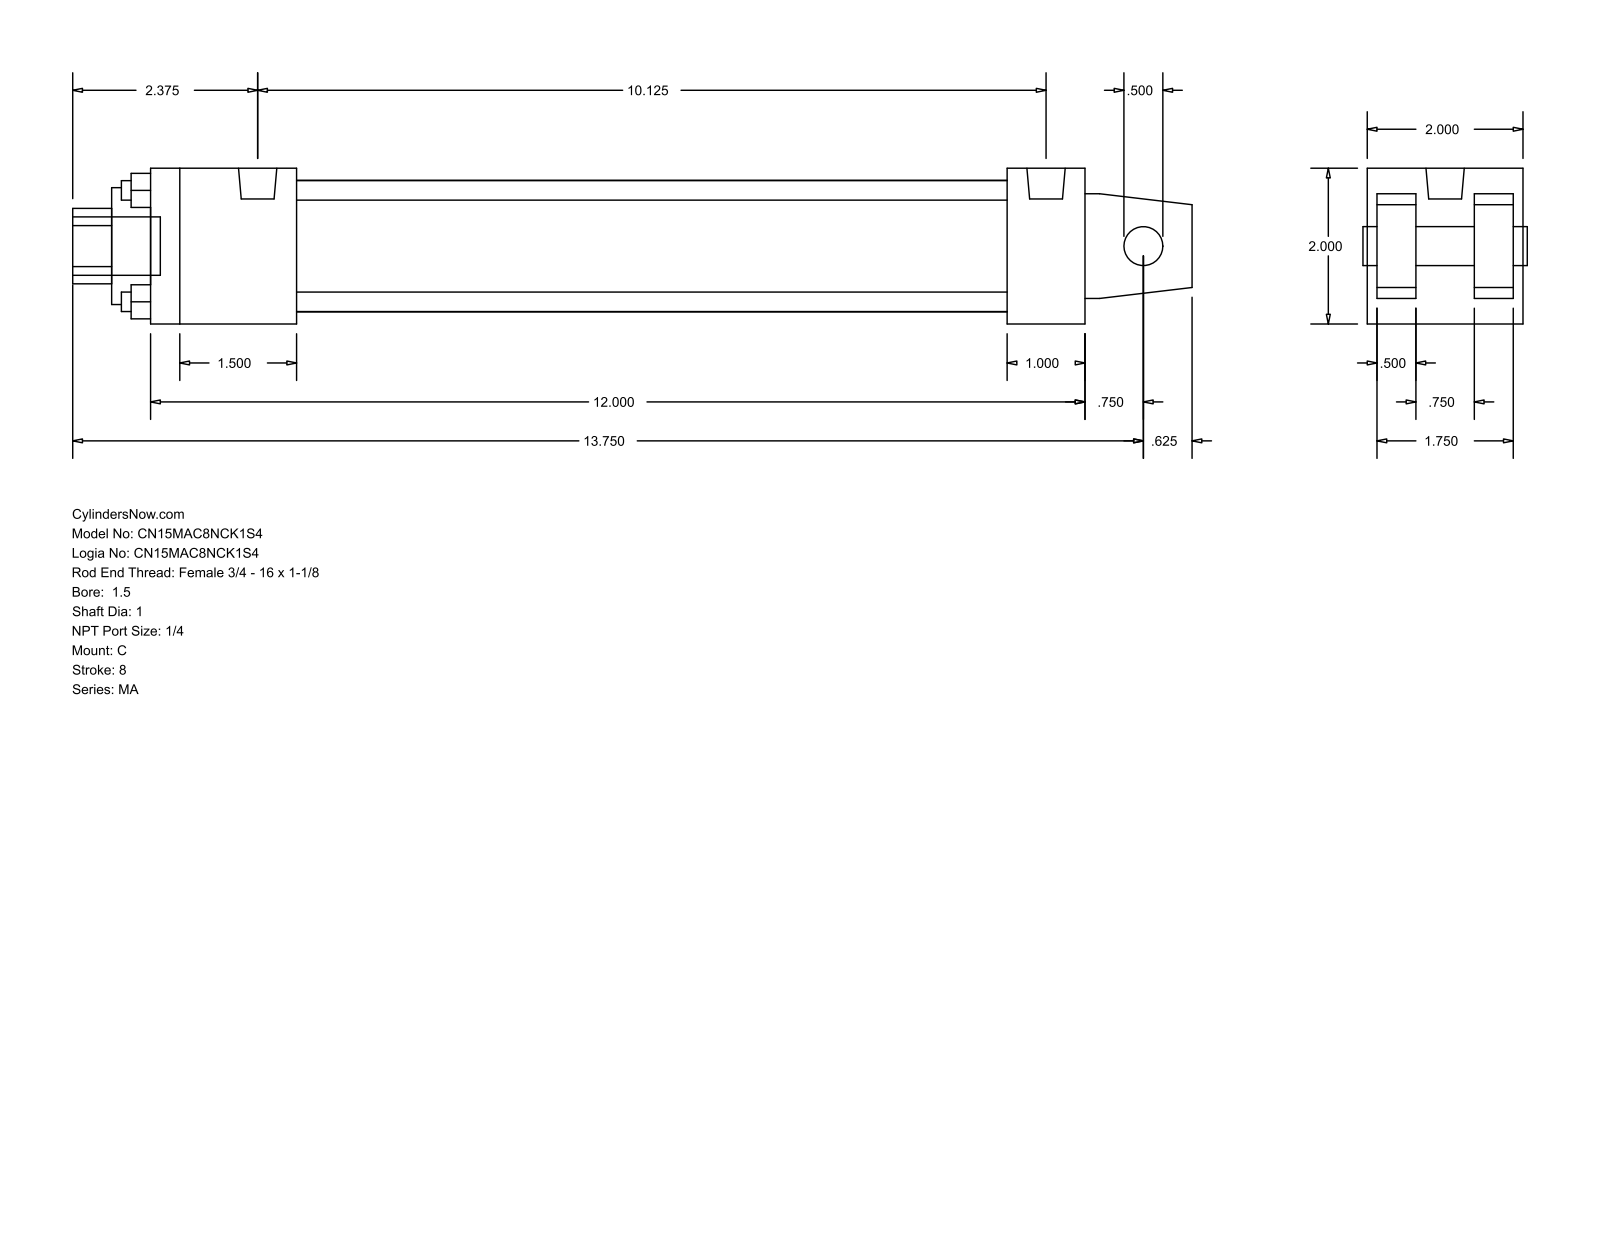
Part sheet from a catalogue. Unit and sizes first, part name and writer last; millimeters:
Units: millimetres
Overall size (bounding box): 365.12 × 50.8 × 50.8
Round holes (diameter × count): ⌀6.35 ×4, ⌀12.7 ×1, ⌀25.4 ×1, ⌀38.1 ×1, ⌀42.93 ×1
Round bosses / shafts (diameter × count): ⌀7.94 ×4, ⌀12.49 ×2, ⌀19.05 ×1
Partial cylindrical surfaces — rounded edges, fillets, slot ends (radius × count): R12.29 ×1
Main face-to-face distances: 50.8, 47.63, 12.7, 3.17, 15.87, 34.93, 31.76, 44.46, 304.8, 25.4
Hole centre spacings: 25.68, 36.32, 51.36
Bodies: 0 solids, 103 faces (76 planar, 27 cylindrical, 0 other)
Part name (STEP PRODUCT): MA_C__0150_1
STEP written by: GSSL Pune (CONFIG_CONTROL_DESIGN)
